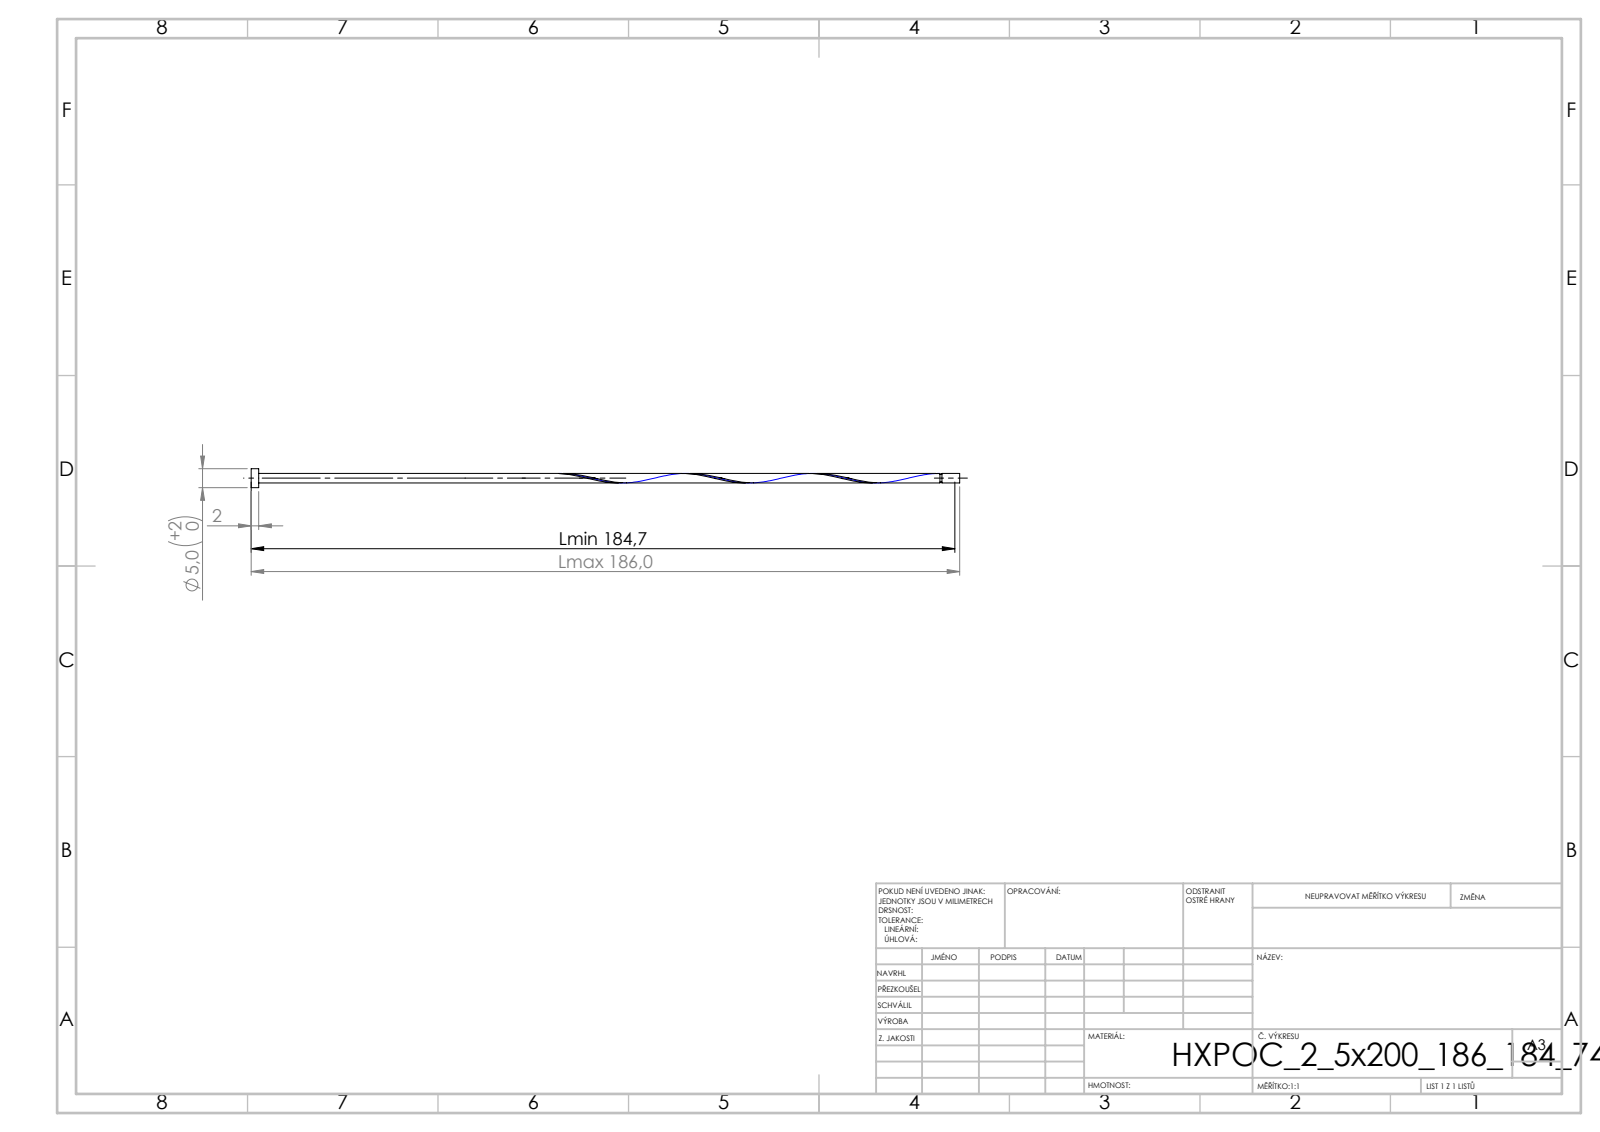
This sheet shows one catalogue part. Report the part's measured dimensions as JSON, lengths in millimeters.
{"step_written_by": "SolidWorks 2019 (CONFIG_CONTROL_DESIGN)", "units": "millimeters", "bodies": {"solids": 1, "faces": 16, "planar": 6, "cylindrical": 9, "other": 1}, "overall_size": [186, 5, 5], "volume_mm3": 1151, "surface_area_mm2": 2067, "round_bosses_or_shafts": [[5, 1], [2.5, 1], [2, 1]], "face_to_face_distances": [2, 186, 184, 181.32, 179.32, 4.68, 180.82, 178.82, 0.5, 5.18]}
